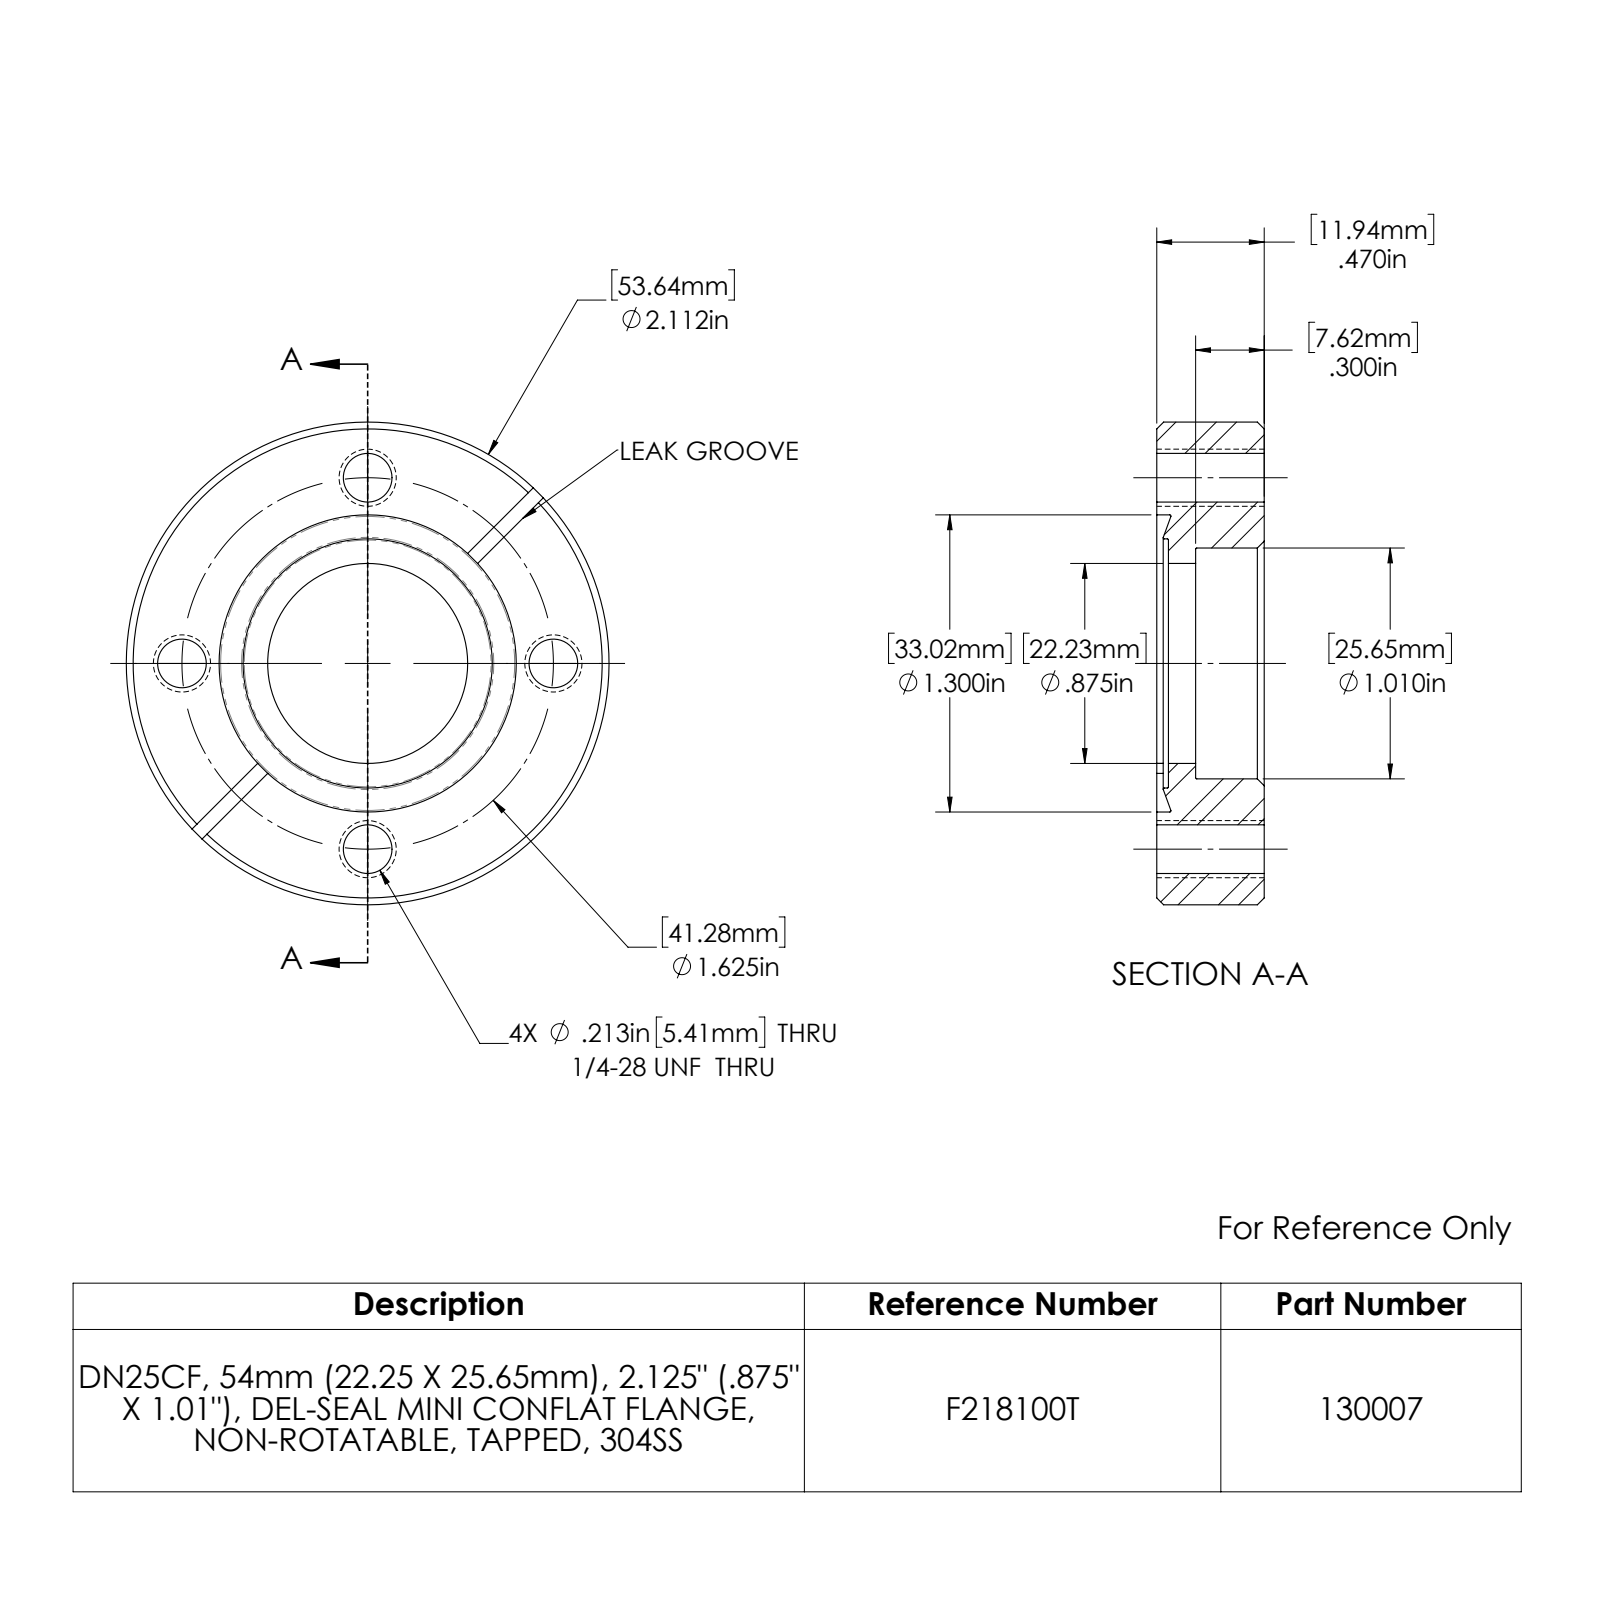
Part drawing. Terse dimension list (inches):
name: 130007_C
written by: SolidWorks 2022 (CONFIG_CONTROL_DESIGN)
unit: in
bodies: 1 solid, 46 faces (9 planar, 20 cylindrical, 17 other)
size: 2.112 × 2.112 × 0.47
volume: 1.189 in³; area: 11.36 in²
holes: 4× ⌀0.213, 1× ⌀0.875, 1× ⌀1.01, 1× ⌀1.09, 1× ⌀1.3
bosses: 1× ⌀2.112
rounds: 2× R1.25
face distances: 0.47, 0.051, 0.419, 0.17, 0.119, 0.3, 0.062
hole spacings: 0.813, 1.149, 1.625
